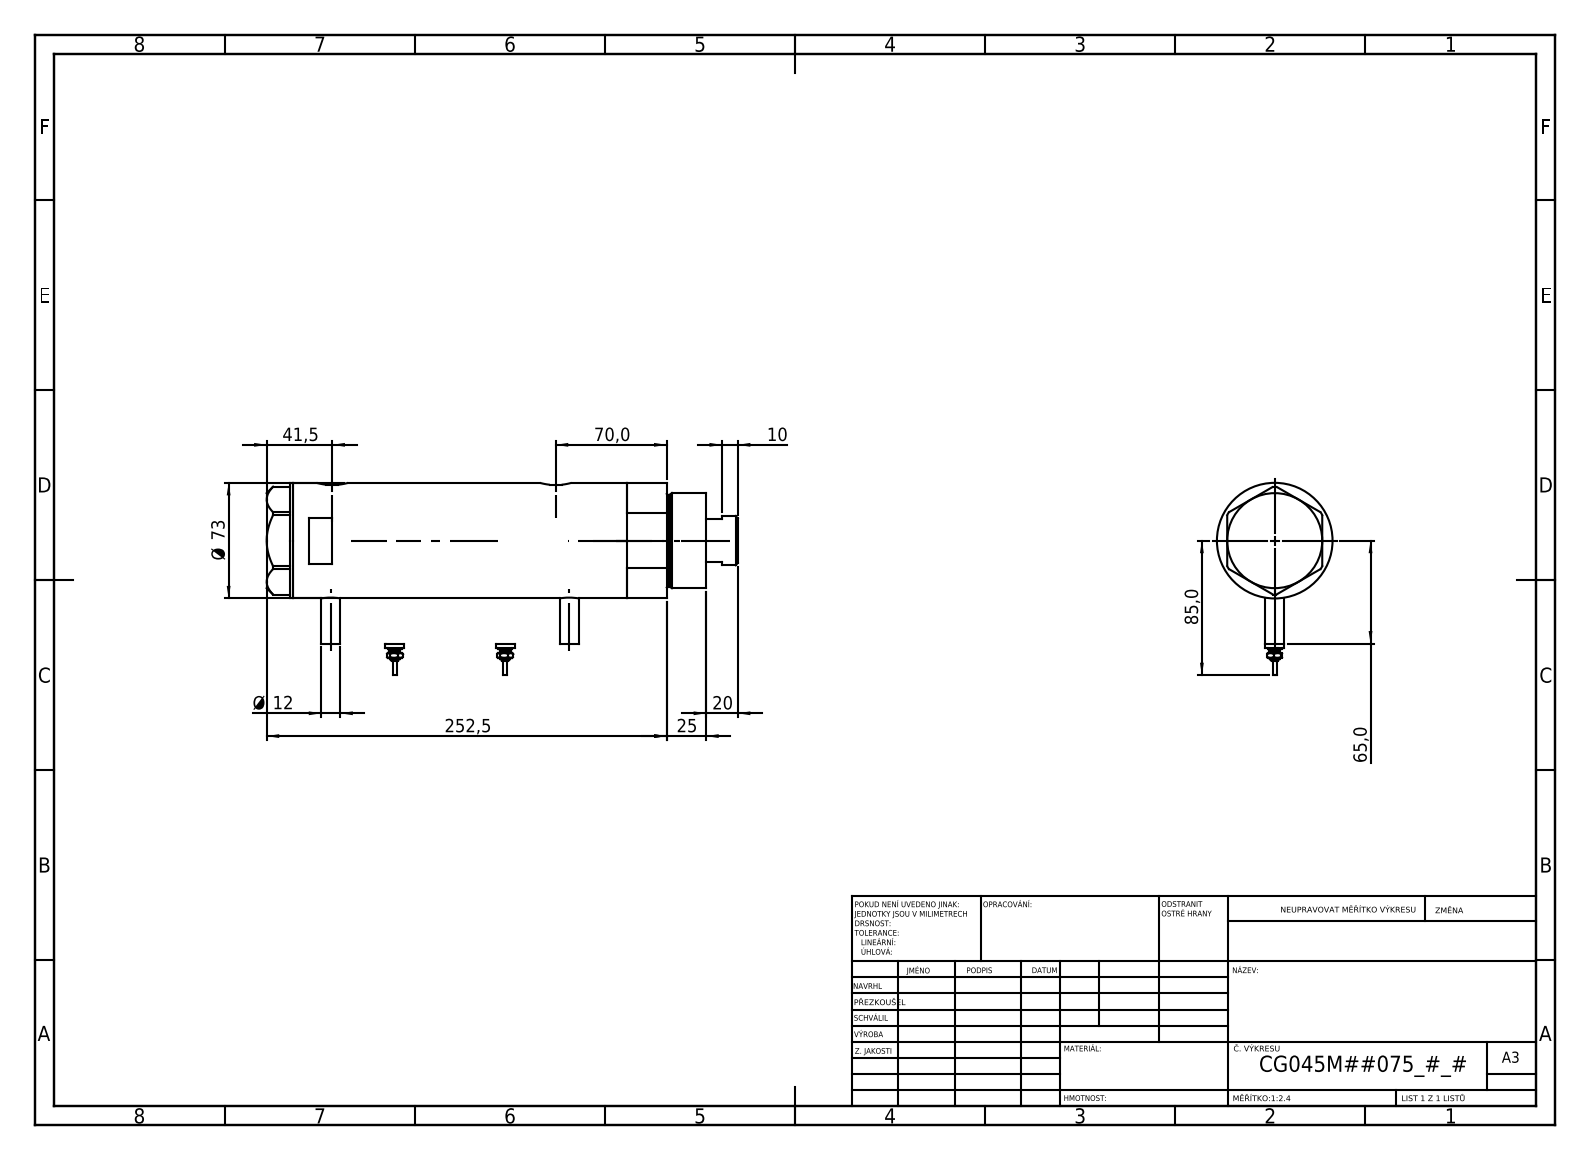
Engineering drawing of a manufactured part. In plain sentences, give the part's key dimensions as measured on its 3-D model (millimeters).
The part is named "V270CG_BACK; V270CG_MIDDLE; V270CG_FRONT; V270CG_VC (+1 more)". Its 3-D file was written by "SolidWorks 2019 (CONFIG_CONTROL_DESIGN)". It is 6 solids with 212 faces: 77 planar, 71 cylindrical and 64 other. Overall it measures 297.5 by 121.5 by 73 millimeters. Its volume is 1 061 000 cubic millimeters and its surface area 173 752 square millimeters. Round holes: 2 of diameter 12.5, 2 of diameter 13.16, 1 of diameter 10.5, 1 of diameter 32, 1 of diameter 33.5, 1 of diameter 45, 1 of diameter 48, 1 of diameter 64. Round bosses or shafts: 4 of diameter 12, 2 of diameter 9, 2 of diameter 7, 2 of diameter 4.5, 2 of diameter 2.5, 1 of diameter 73, 1 of diameter 60, 1 of diameter 58. Partial cylindrical surfaces (rounded edges, fillets, slot ends): 2 of radius 10. The main face-to-face distances are 166, 26, 140, 16.5, 42.5, 182.5, 2, 261, 277.5, 235. The hole center spacings are 1, 8.5, 141, 142, 149.5, 150.5.
